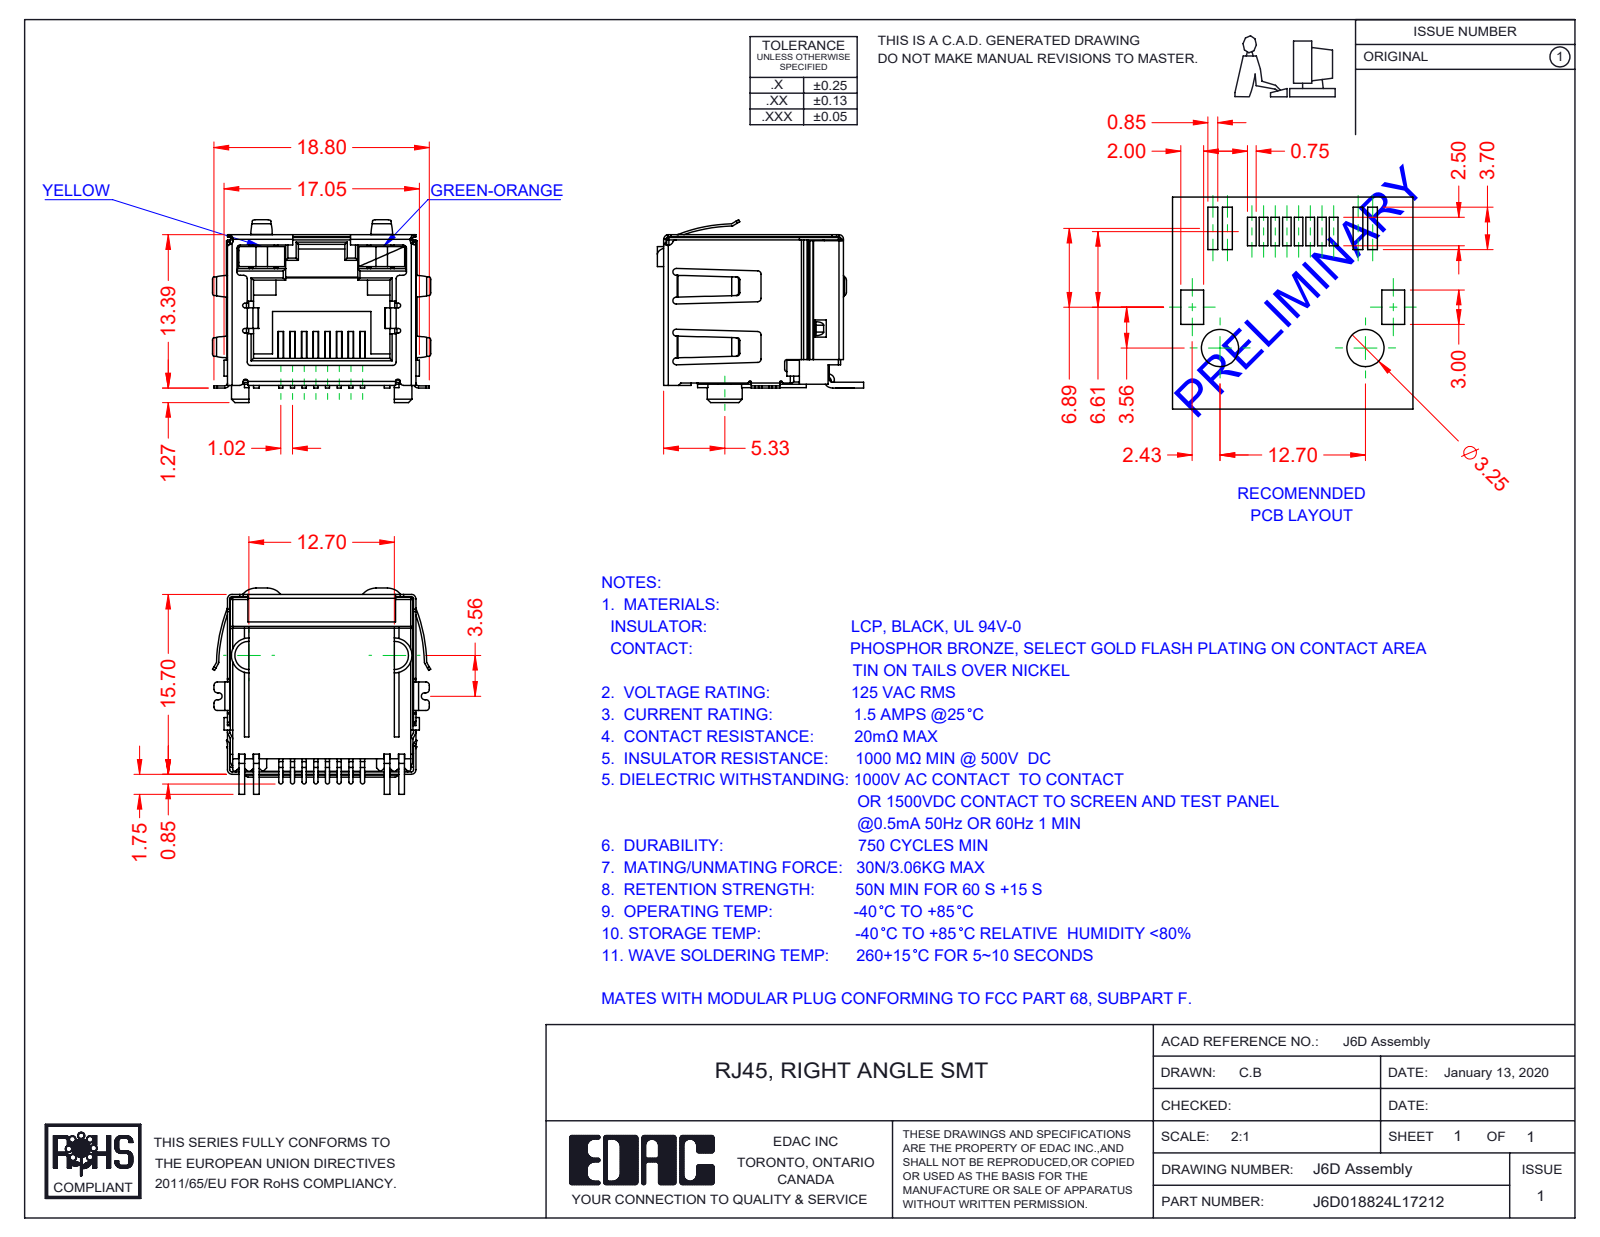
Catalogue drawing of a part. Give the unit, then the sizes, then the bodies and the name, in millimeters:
Units: millimetres
Overall size (bounding box): 19.06 × 18 × 15.95
Partial cylindrical surfaces — rounded edges, fillets, slot ends (radius × count): R0.3 ×55, R0.2 ×40, R0.4 ×19, R0.25 ×16, R0.1 ×12, R0.15 ×8, R0.18 ×8, R0.5 ×6
Main face-to-face distances: 16, 16.2, 16.25, 2.25, 1, 15.95, 12.8, 0.45, 13.05, 10.6
Volume: 1 790 mm³ · Surface area: 4 796 mm²
Bodies: 12 solids, 1031 faces (702 planar, 284 cylindrical, 45 other)
Part name (STEP PRODUCT): 6D LED RH_7-Green-Orange; 6D Shield_LED - EMI; J6D018824L17212; 6D Insulator (+2 more)
STEP written by: SolidWorks 2016 (CONFIG_CONTROL_DESIGN)
